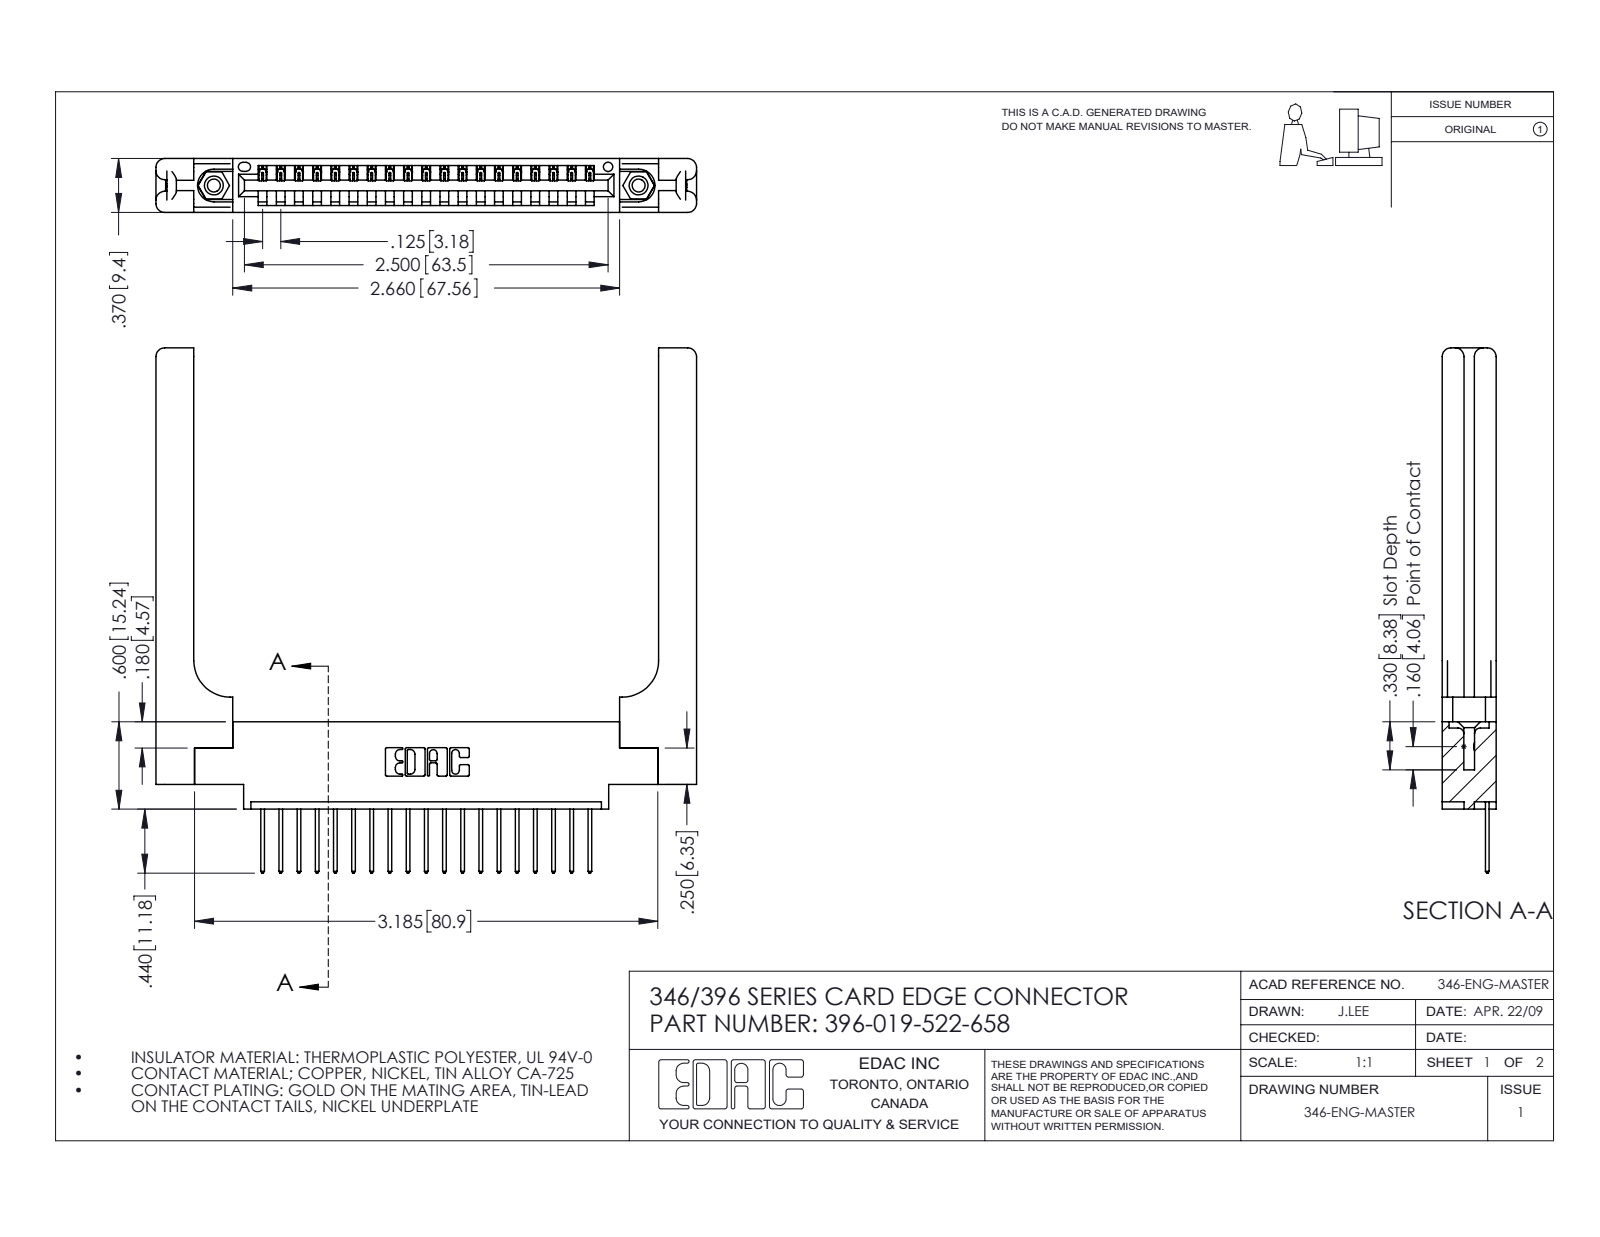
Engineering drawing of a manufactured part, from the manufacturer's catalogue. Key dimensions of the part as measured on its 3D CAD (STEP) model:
Part name (STEP PRODUCT): 346 Part_0.170 Offset - 0.156 Dia-TH; 396-019-522-658; 346-220-058_345-220-058; 345-250-001_345-250-001-102 (+1 more)
STEP written by: SolidWorks 2016 (CONFIG_CONTROL_DESIGN)
Units: inches
Bodies: 24 solids, 1484 faces (988 planar, 436 cylindrical, 60 other)
Overall size (bounding box): 3.716 × 3.61 × 0.37
Volume: 0.991 in³ · Surface area: 24.89 in²
Round holes (diameter × count): ⌀0.089 ×2, ⌀0.125 ×2, ⌀0.156 ×2, ⌀0.064 ×1
Round bosses / shafts (diameter × count): ⌀0.155 ×2
Partial cylindrical surfaces — rounded edges, fillets, slot ends (radius × count): R0.006 ×38, R0.01 ×38, R0.01 ×22, R0.06 ×16, R0.007 ×6, R0.031 ×6, R0.026 ×3, R0.03 ×2
Main face-to-face distances: 0.37, 0.072, 0.15, 0.048, 0.322, 0.148, 0.25, 0.298, 0.025, 0.102
Hole centre spacings: 0.246, 2.713, 2.92
